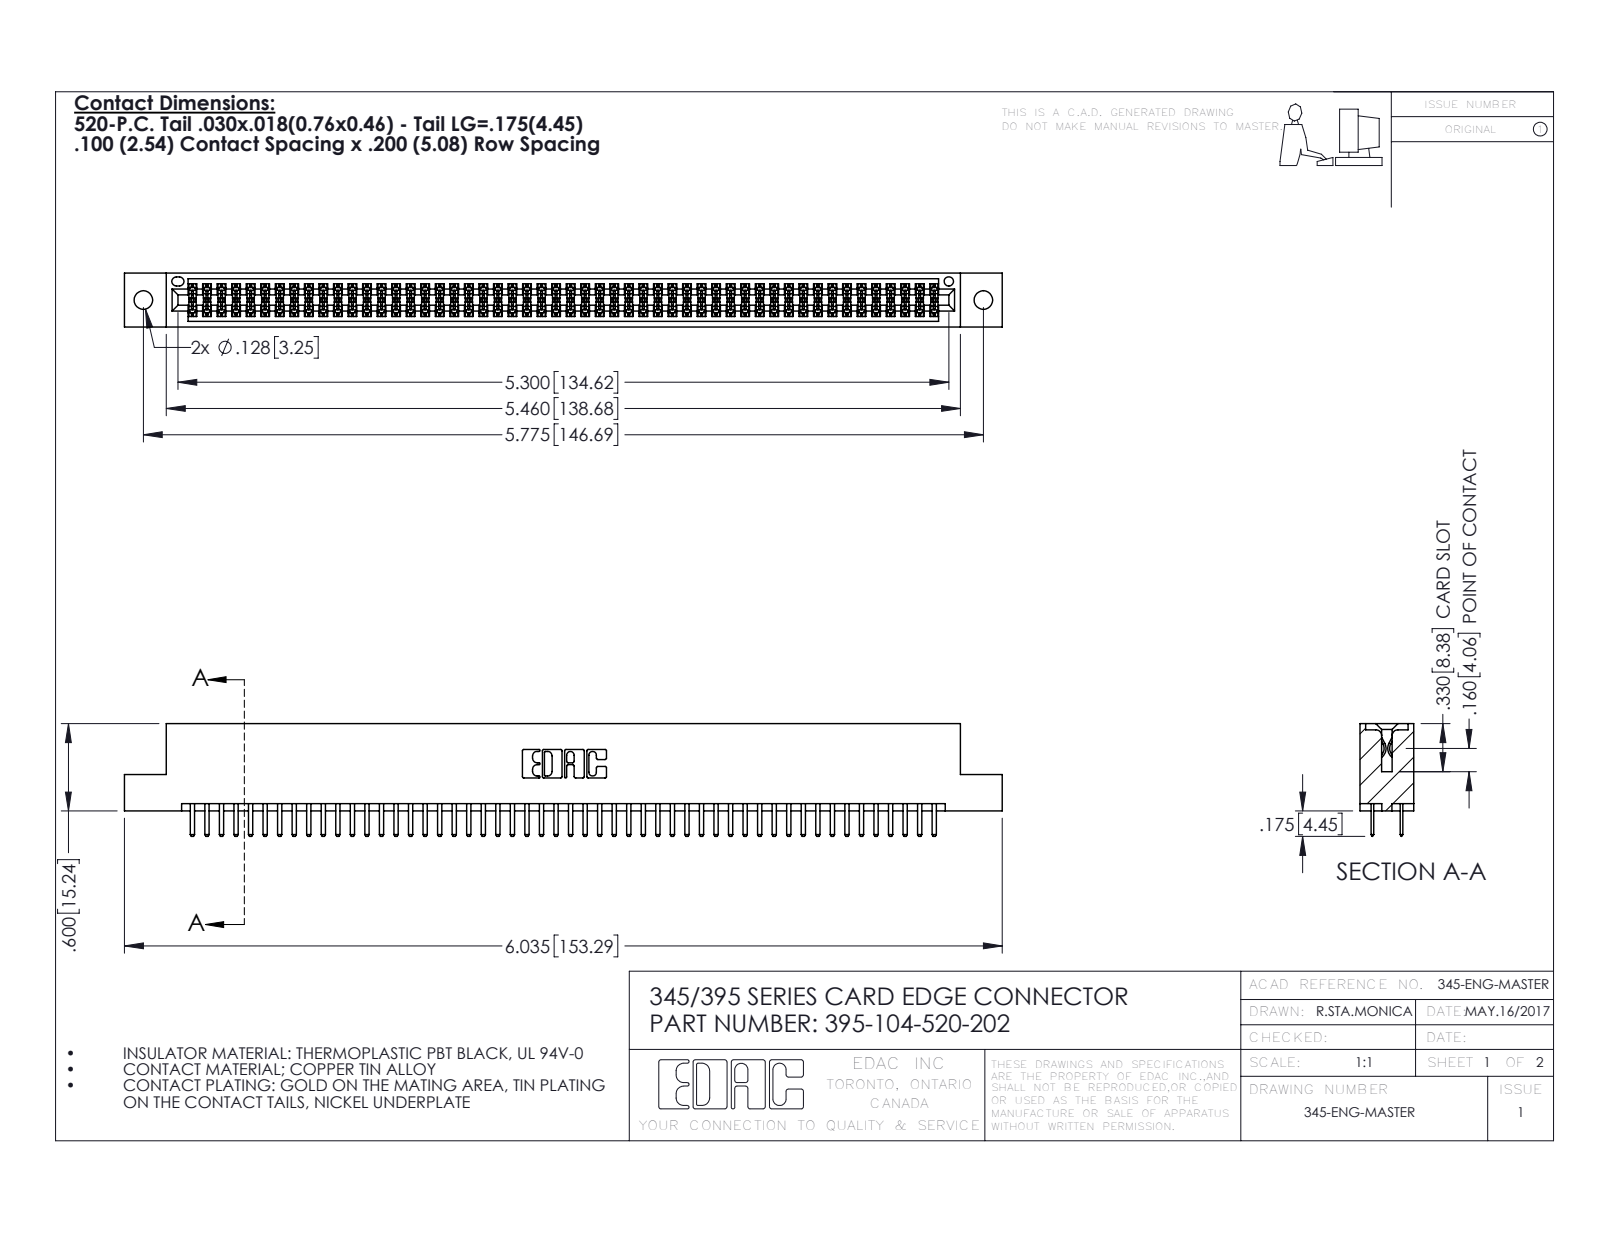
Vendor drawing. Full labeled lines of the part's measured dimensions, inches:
Part name (STEP PRODUCT): 395-104-520-202; 345 Part_Flush Mounting Lugs - 0.128 Dia; 345-292-001_345-293-120
STEP written by: SolidWorks 2016 (CONFIG_CONTROL_DESIGN)
Units: inches
Bodies: 105 solids, 5742 faces (3720 planar, 2022 cylindrical, 0 other)
Overall size (bounding box): 6.035 × 0.775 × 0.37
Volume: 0.909 in³ · Surface area: 33.87 in²
Round holes (diameter × count): ⌀0.128 ×2, ⌀0.064 ×1
Partial cylindrical surfaces — rounded edges, fillets, slot ends (radius × count): R0.006 ×156, R0.01 ×108, R0.01 ×22, R0.007 ×6, R0.031 ×6, R0.026 ×3, R0.014 ×2, R0.019 ×2
Main face-to-face distances: 0.298, 0.072, 0.2, 0.37, 0.098, 0.272, 0.025, 0.225, 0.022, 0.072
Hole centre spacings: 0.27, 5.539, 5.775
